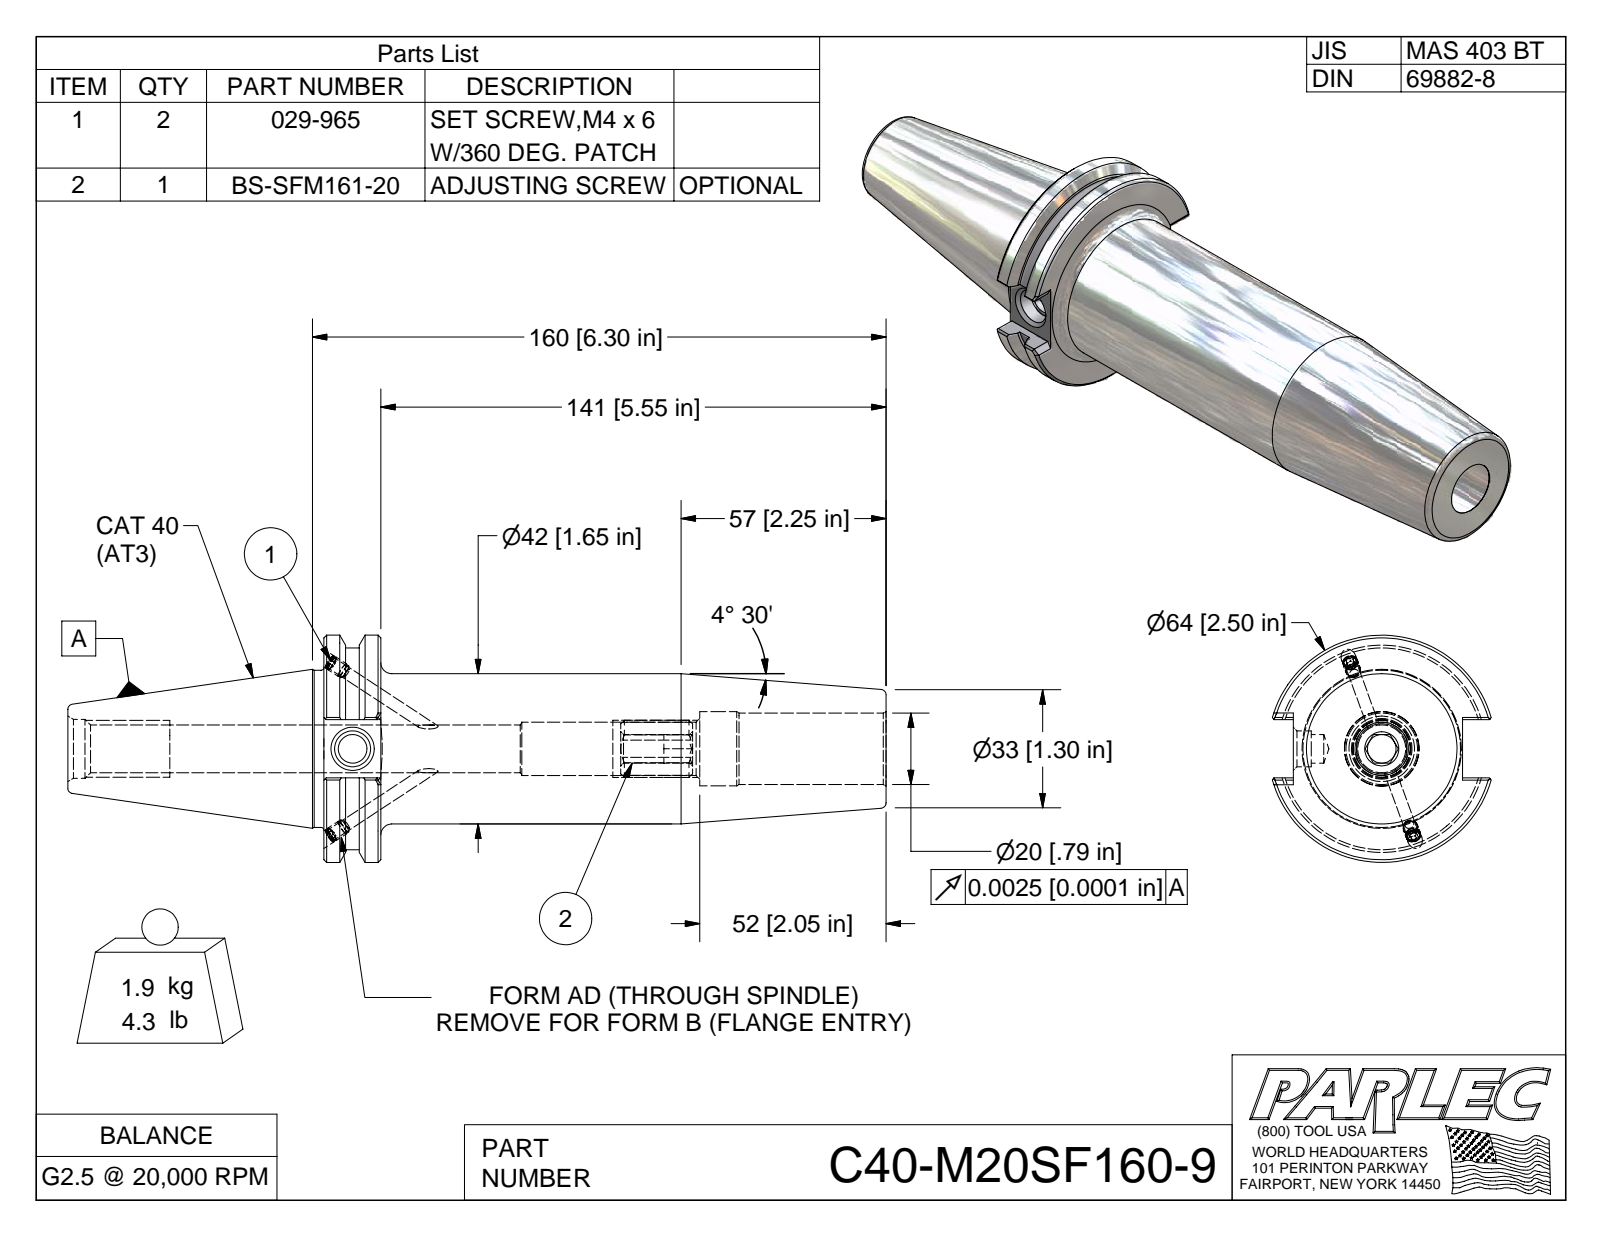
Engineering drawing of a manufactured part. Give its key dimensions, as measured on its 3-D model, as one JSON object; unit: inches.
{"part_name": "C40-M20SF160-9; C40BC-M20SF160-9-1; 029-965; BS-SFM161-20", "step_written_by": "Autodesk Inventor 2009 (AUTOMOTIVE_DESIGN)", "units": "inches", "bodies": {"solids": 4, "faces": 132, "planar": 66, "cylindrical": 22, "other": 44}, "overall_size": [8.987, 2.5, 2.403], "volume_in3": 15.35, "surface_area_in2": 73.57, "round_holes": [[0.13, 2], [0.161, 2], [0.786, 1], [0.816, 1]], "round_bosses_or_shafts": [[0.165, 2], [0.157, 2], [2.5, 1], [2.219, 1], [1.73, 1], [1.654, 1]], "partial_cylinders_radius": [[0.315, 1]], "face_to_face_distances": [0.625, 6.175, 5.55, 6.174, 5.549, 0.64, 1.164, 0.613, 0.551, 1.86]}
